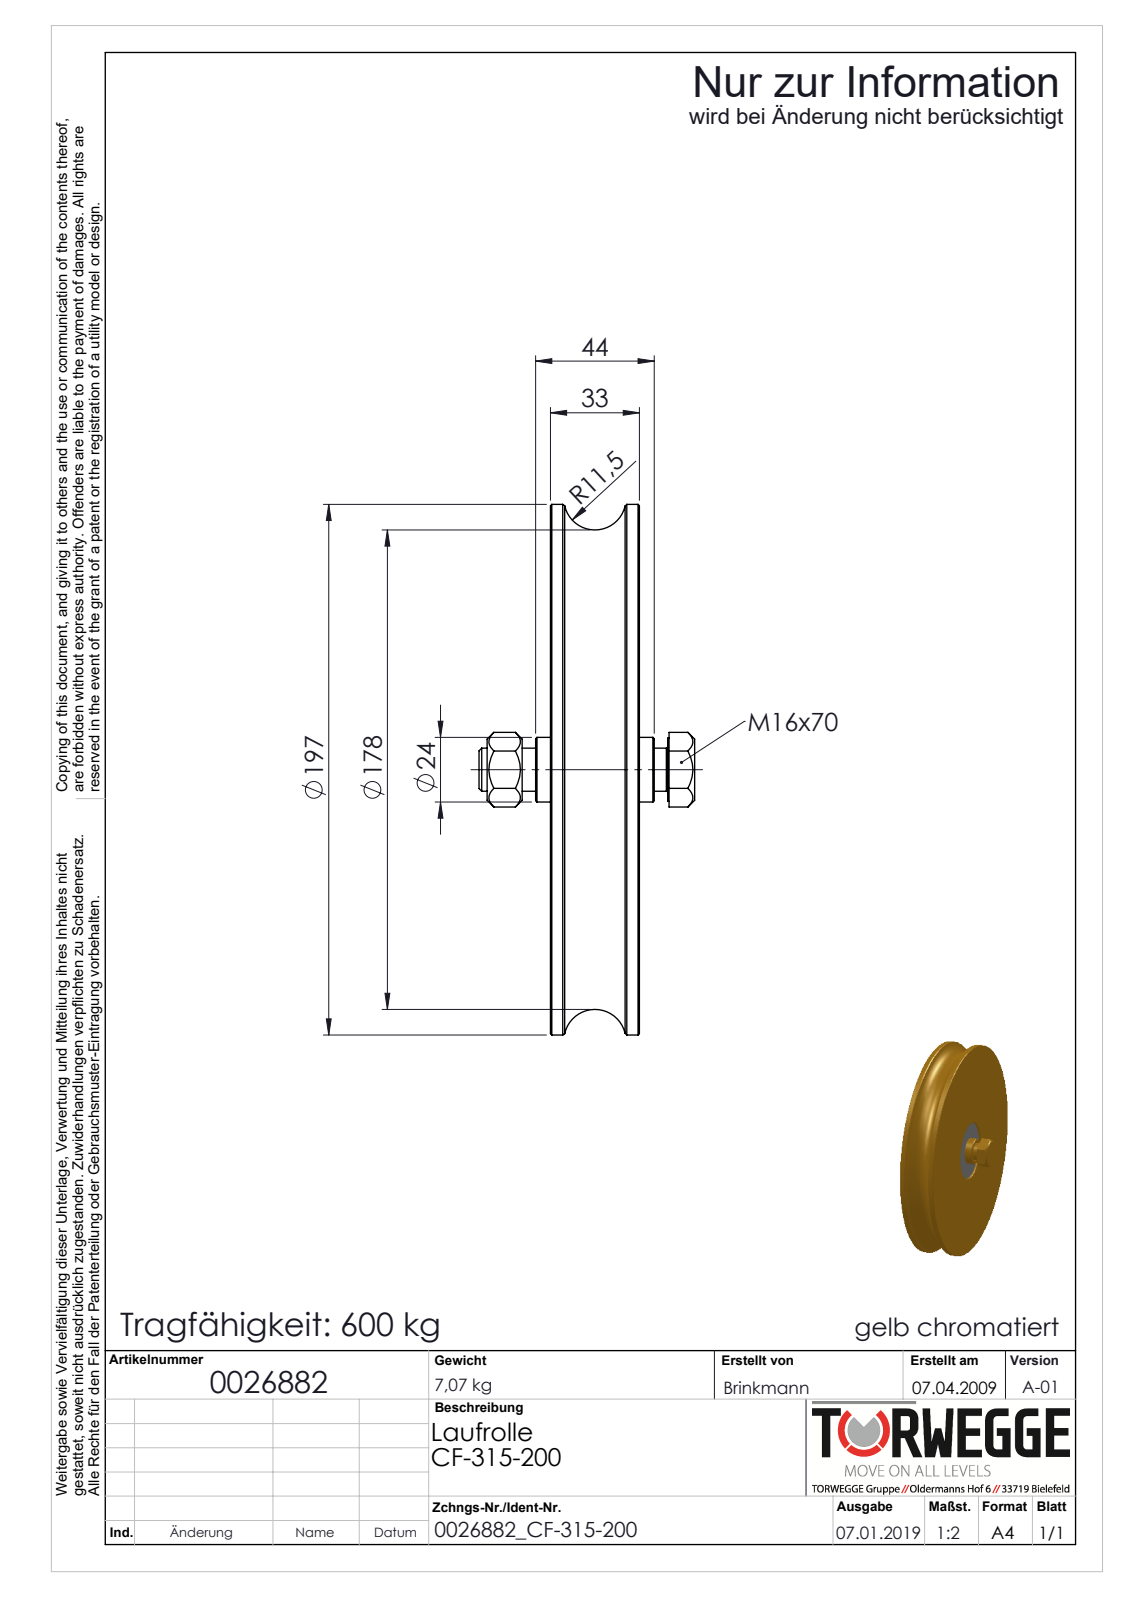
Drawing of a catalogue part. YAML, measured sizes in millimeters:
part_name: "0026882_CF-315-200_(A-01)"
step_written_by: "SolidWorks 2018 (AUTOMOTIVE_DESIGN)"
units: millimeters
bodies: {solids: 5, faces: 114, planar: 28, cylindrical: 30, other: 56}
overall_size: [197, 197, 80]
volume: 922766
surface_area: 98863
round_holes:
  - {diameter: 13.84, count: 1}
  - {diameter: 16.2, count: 1}
  - {diameter: 20, count: 1}
  - {diameter: 44, count: 1}
  - {diameter: 52, count: 1}
round_bosses_or_shafts:
  - {diameter: 197, count: 1}
  - {diameter: 24, count: 1}
  - {diameter: 23.5, count: 1}
  - {diameter: 16, count: 1}
face_to_face_distances: [33, 1.5, 31.5, 30, 24, 22, 20.5, 5.5, 10.5, 12]
